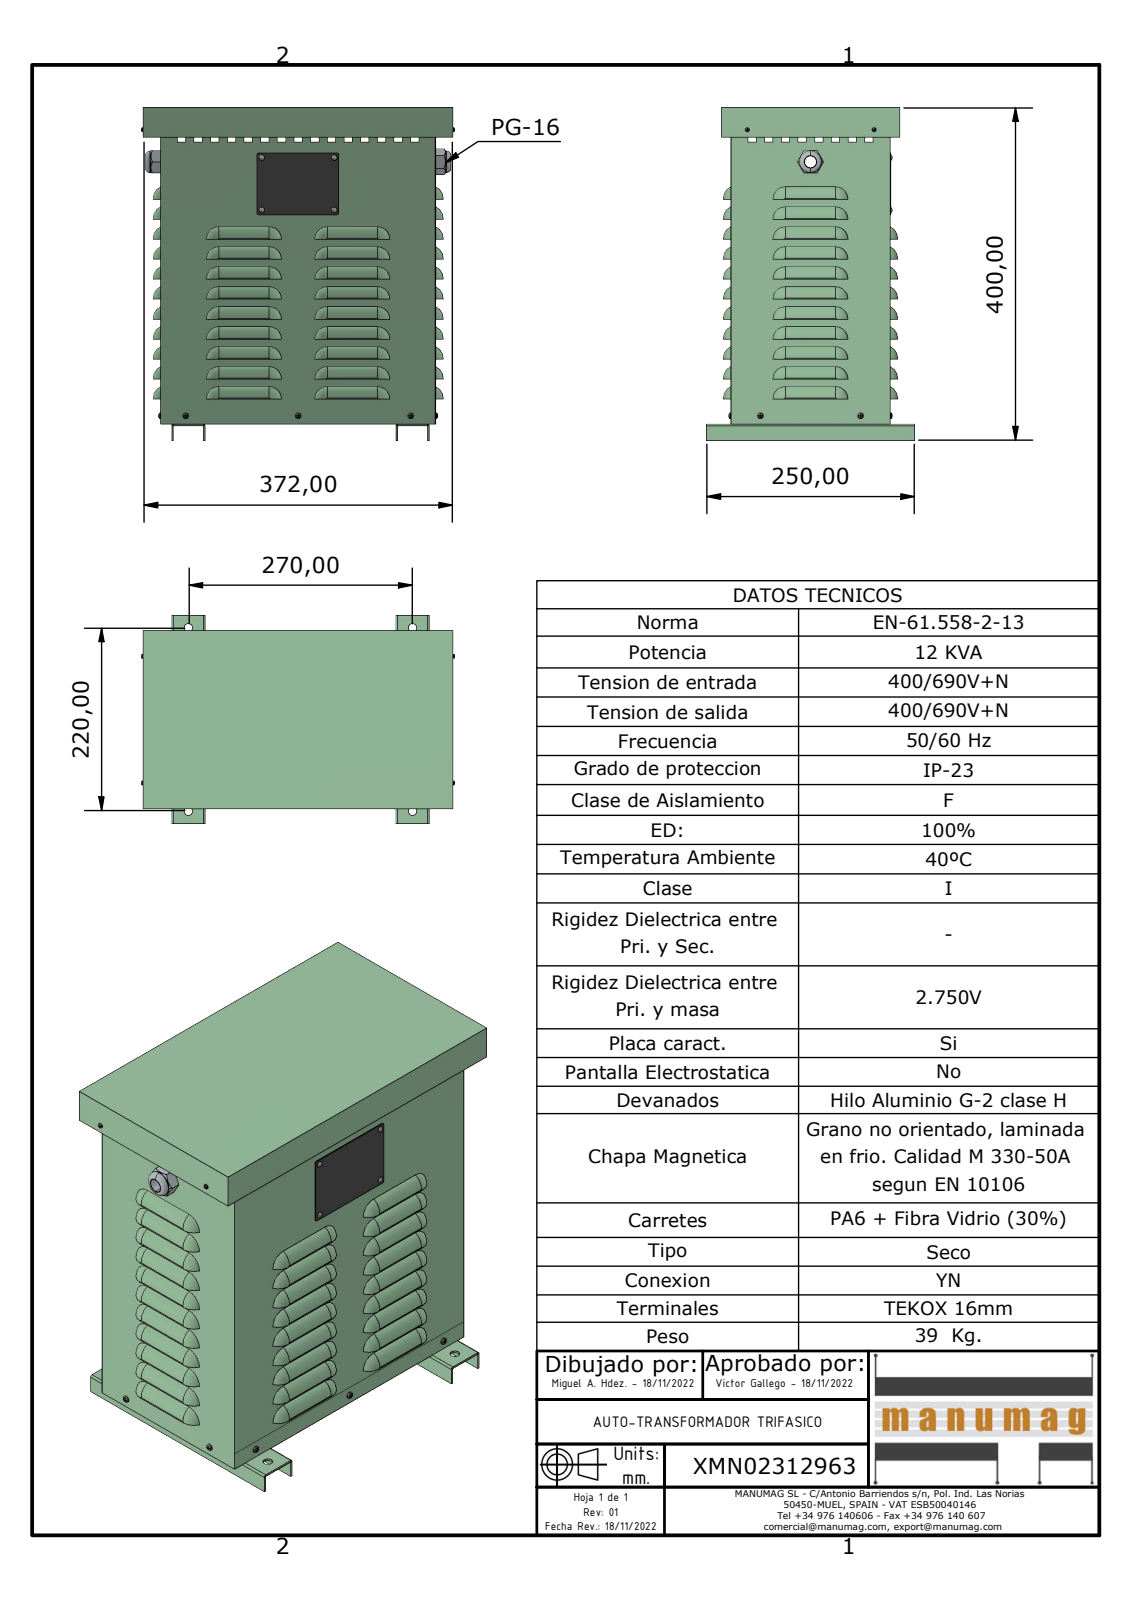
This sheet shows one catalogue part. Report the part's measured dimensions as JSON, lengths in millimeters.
{"part_name": "XMN02312963; JE010 NACIONAL CUERPO; JE010 NACIONAL BASE; PLACA CARACTERISTICAS (+6 more)", "step_written_by": "Autodesk Inventor 2023 (AUTOMOTIVE_DESIGN)", "units": "millimeters", "bodies": {"solids": 26, "faces": 1888, "planar": 958, "cylindrical": 396, "other": 534}, "overall_size": [400.63, 376.16, 250], "volume_mm3": 883061, "surface_area_mm2": 1346000, "round_holes": [[4, 9], [3, 4], [10, 4], [14, 1], [24, 1]], "round_bosses_or_shafts": [[3.5, 5], [3.18, 5], [3.2, 4], [2.5, 2], [2.26, 2], [26, 1], [23, 1], [22.5, 1]], "partial_cylinders_radius": [[14, 66], [7, 42], [15, 42], [1.5, 12], [5, 8], [5.5, 8], [0.5, 5], [0.5, 4]], "face_to_face_distances": [0.5, 190.5, 1.5, 190, 379.12, 329.5, 191, 380.62, 329, 330], "hole_center_spacings": [63, 85.25, 87, 107.42, 135, 152, 220, 250.8]}
